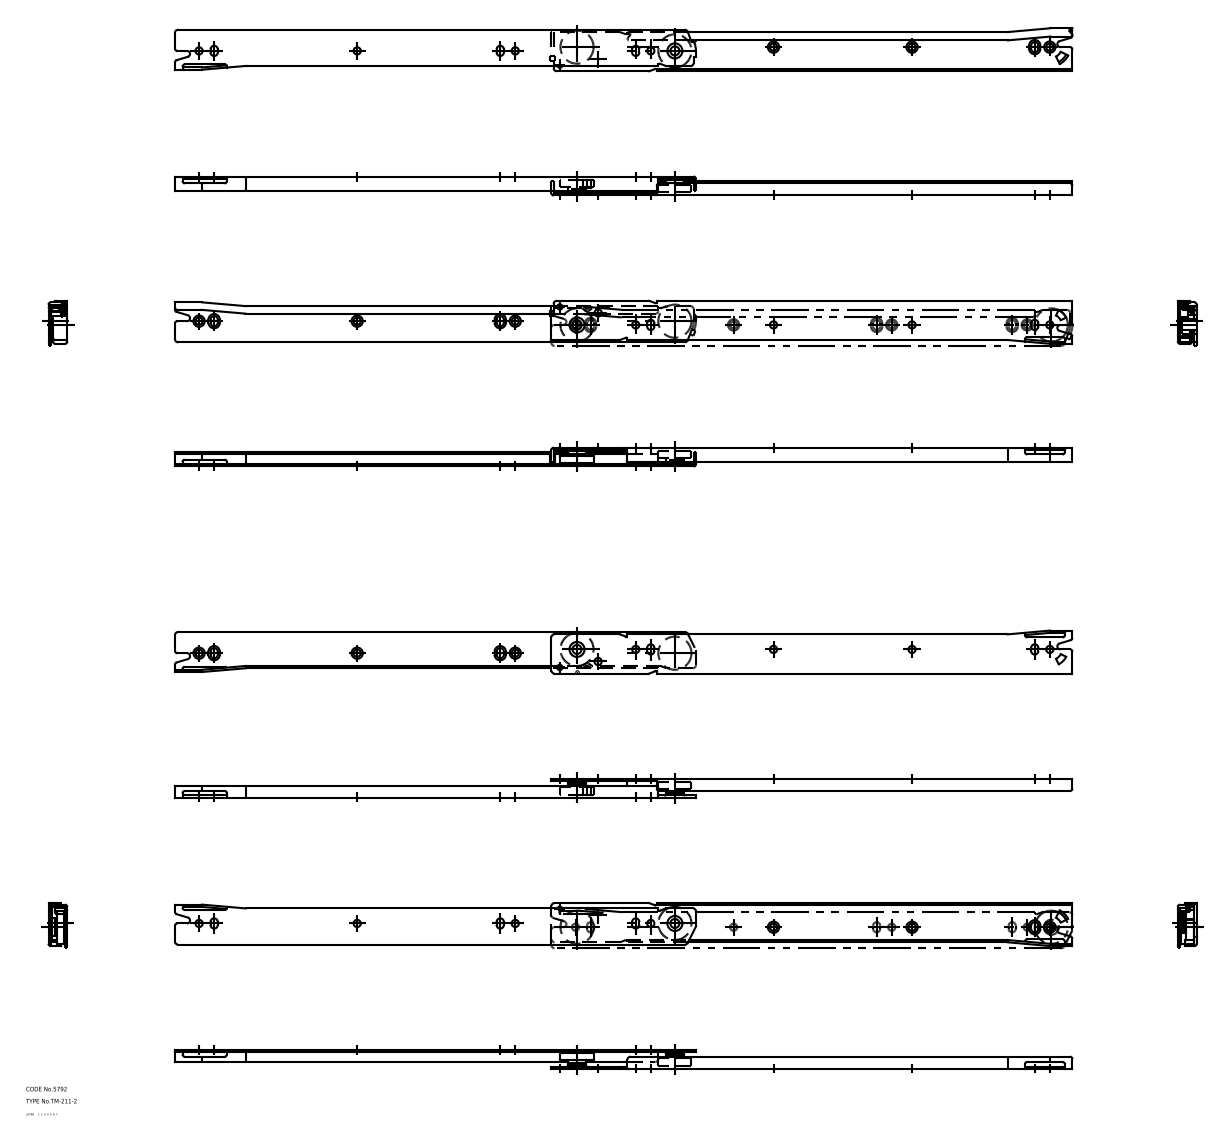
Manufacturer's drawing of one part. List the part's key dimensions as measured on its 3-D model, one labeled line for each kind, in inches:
Part name (STEP PRODUCT): roller; member_B; member_A; TM_211_2_1073_36
STEP written by: CADfix (AUTOMOTIVE_DESIGN)
Units: inches
Bodies: 4 solids, 181 faces (0 planar, 0 cylindrical, 181 other)
Overall size (bounding box): 23.465 × 1.122 × 0.492
Volume: 2.297 in³ · Surface area: 77.19 in²
